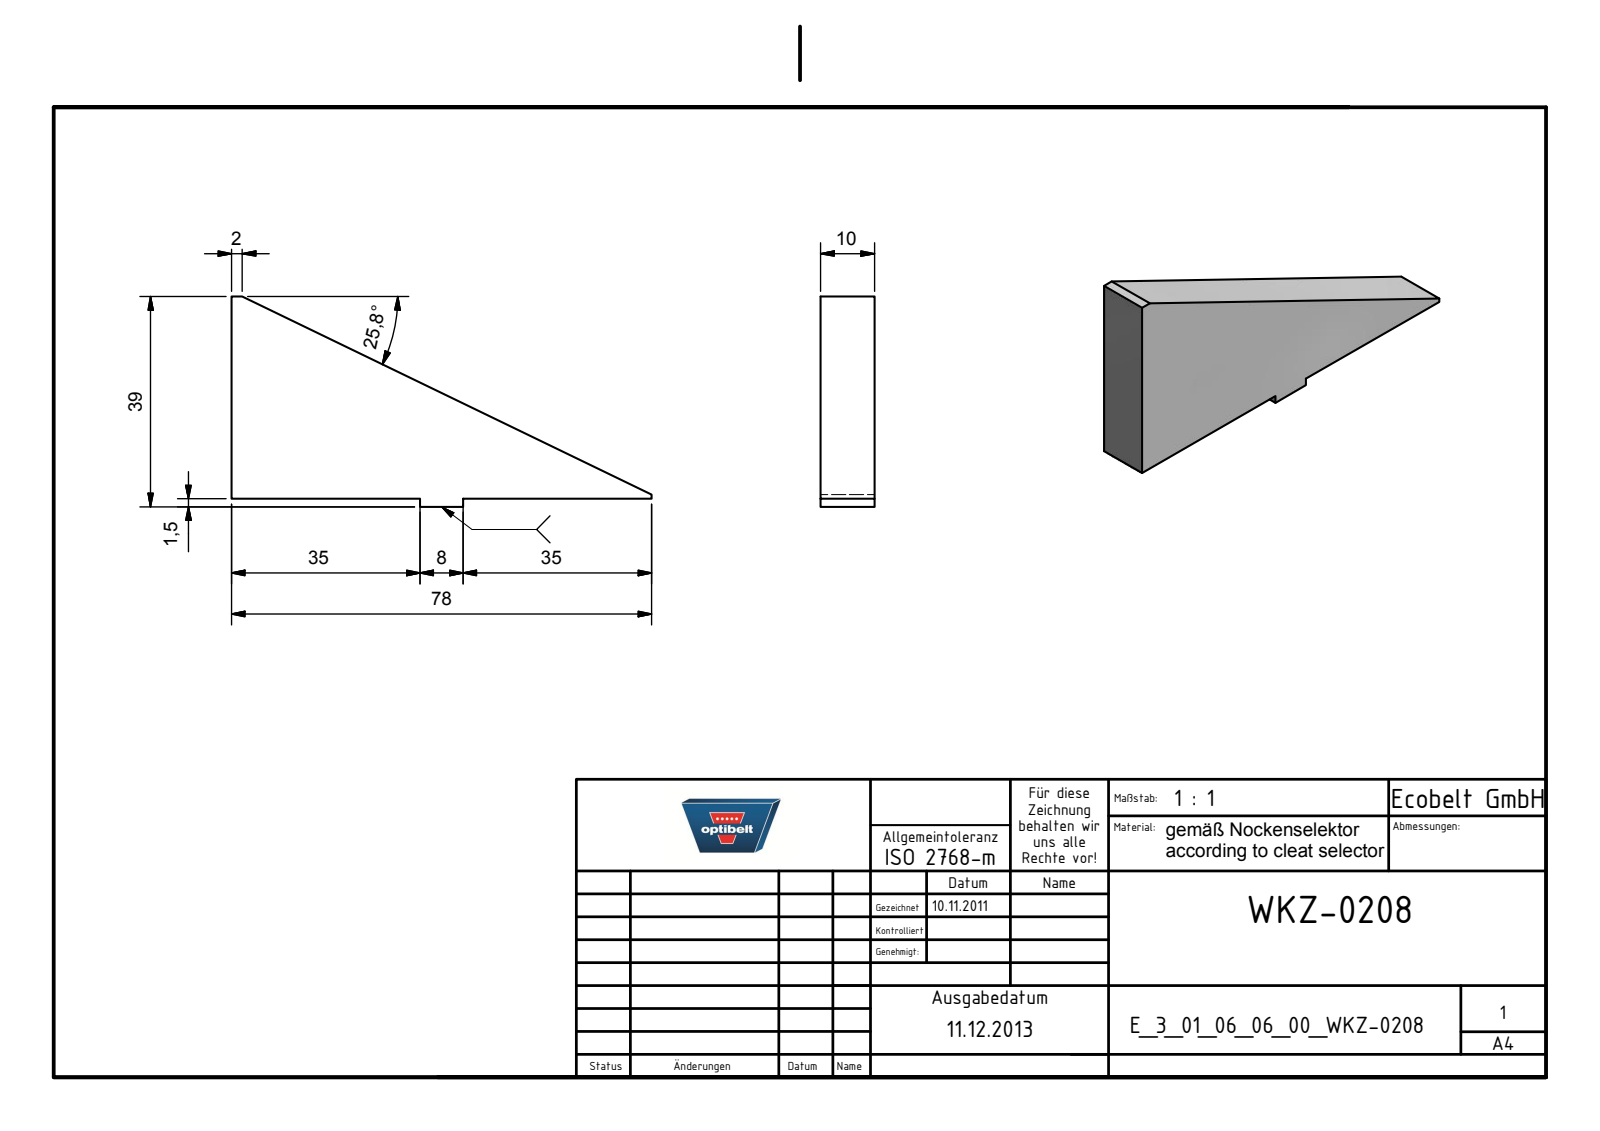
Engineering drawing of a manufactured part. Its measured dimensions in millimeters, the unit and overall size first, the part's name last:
Units: millimetres
Overall size (bounding box): 78 × 39 × 10
Main face-to-face distances: 10, 1.5, 35, 43, 39, 37.5, 8, 78
Volume: 15 409 mm³ · Surface area: 5 139 mm²
Bodies: 1 solid, 11 faces (11 planar, 0 cylindrical, 0 other)
Part name (STEP PRODUCT): E_3_01_06_06_00_WKZ-0208
STEP written by: Autodesk Inventor 2025 (AUTOMOTIVE_DESIGN)
